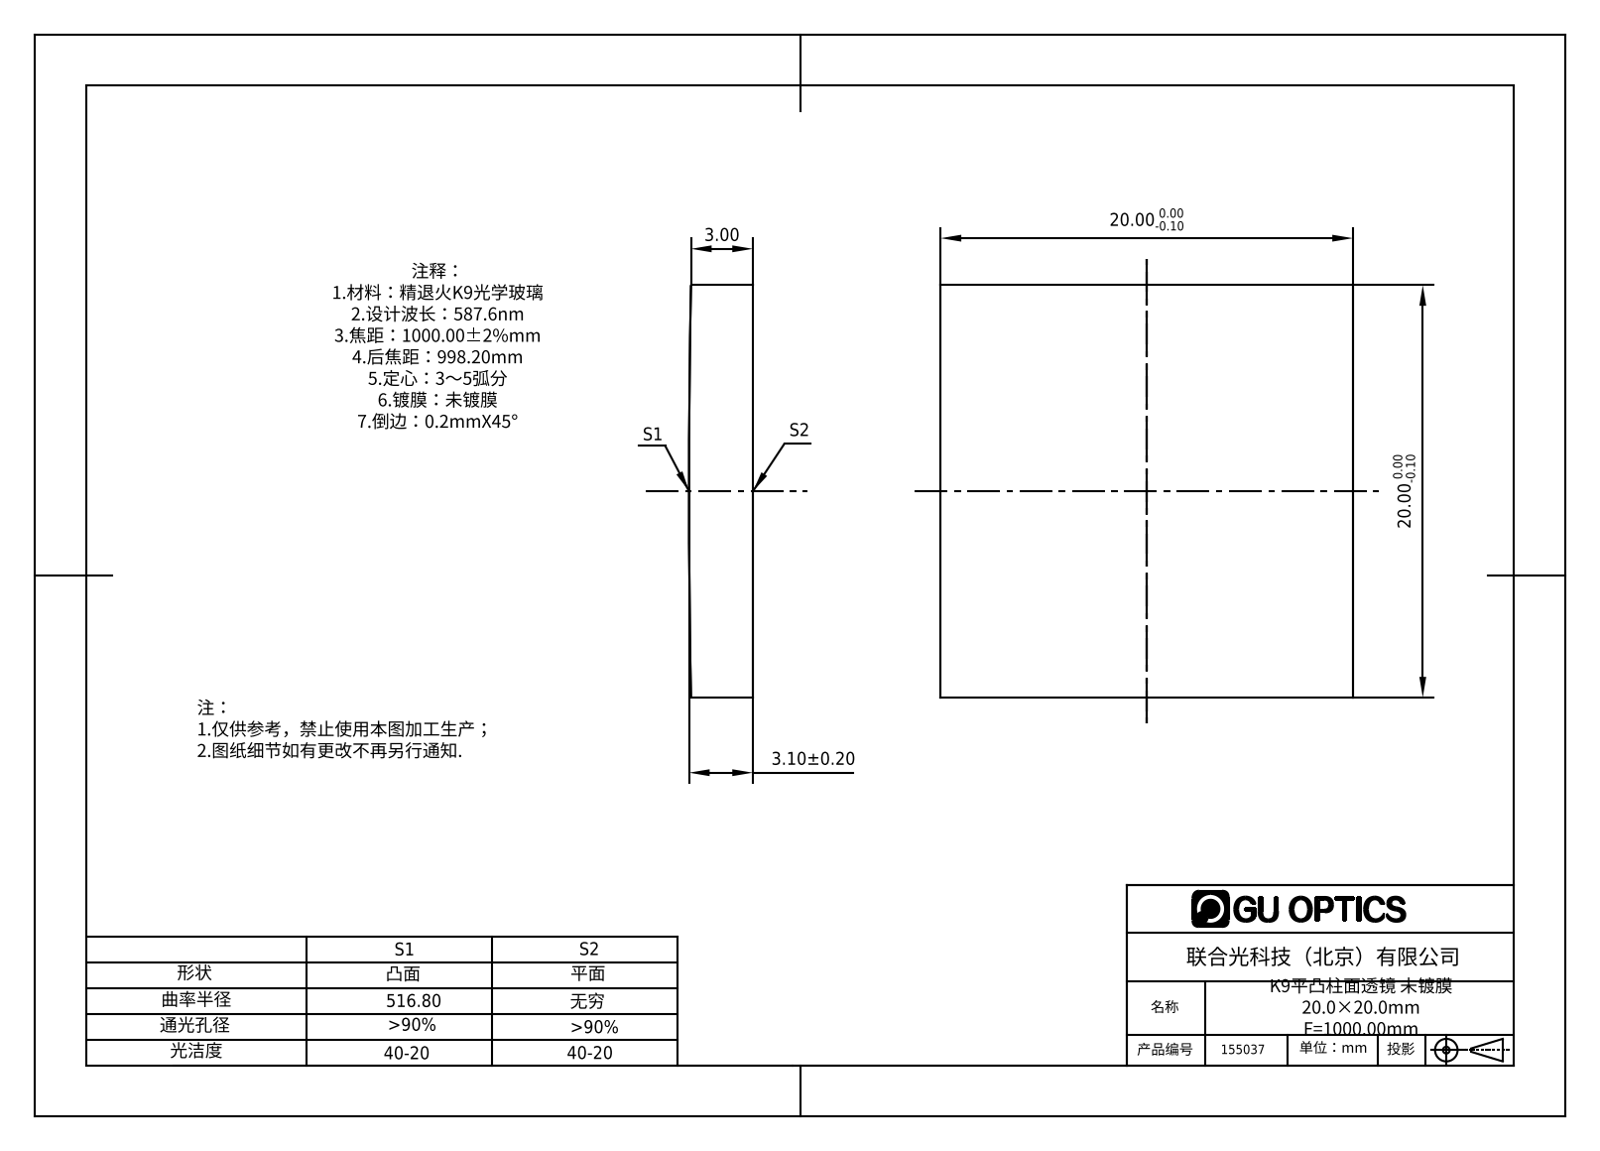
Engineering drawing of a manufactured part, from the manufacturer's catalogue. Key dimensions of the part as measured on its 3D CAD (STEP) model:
Part name (STEP PRODUCT): 155037
STEP written by: SolidWorks 2016 (AUTOMOTIVE_DESIGN)
Units: millimetres
Bodies: 1 solid, 6 faces (5 planar, 1 cylindrical, 0 other)
Overall size (bounding box): 20 × 20 × 3.1
Volume: 1 227 mm³ · Surface area: 1 043 mm²
Partial cylindrical surfaces — rounded edges, fillets, slot ends (radius × count): R516.8 ×1
Main face-to-face distances: 20
